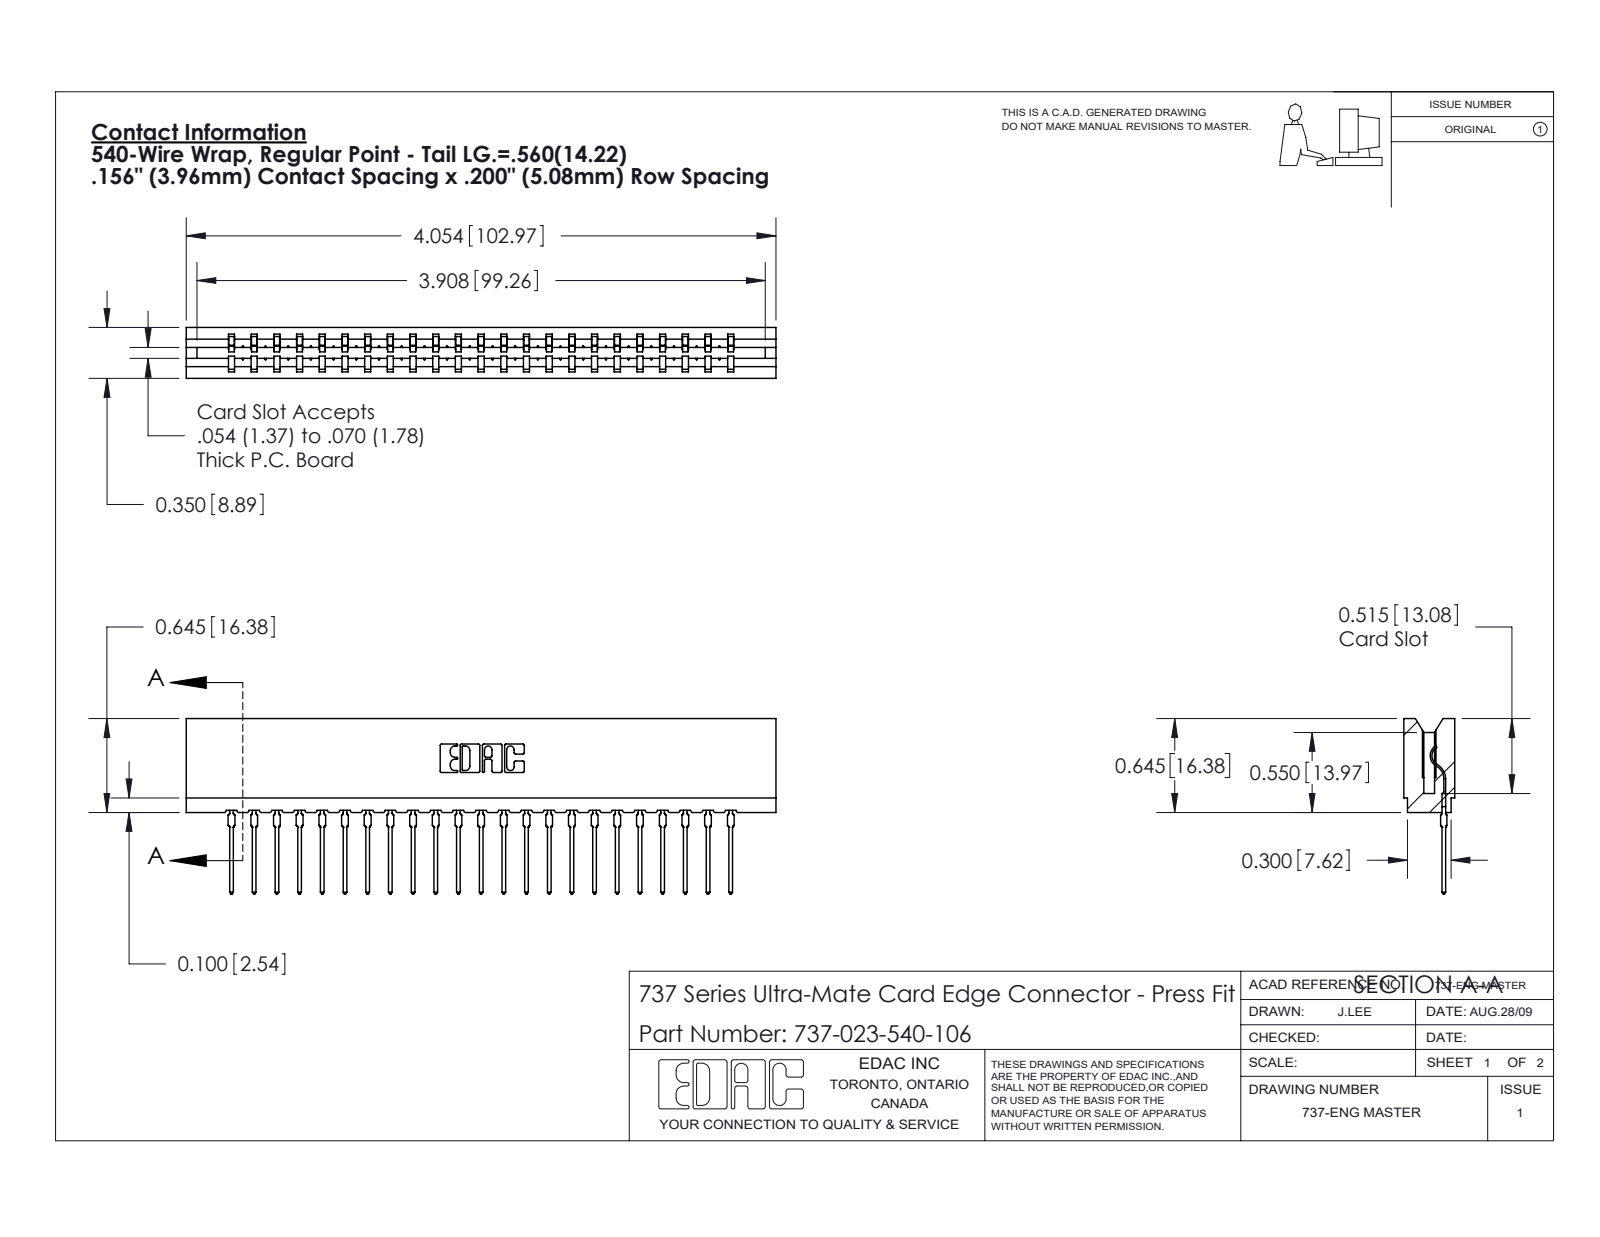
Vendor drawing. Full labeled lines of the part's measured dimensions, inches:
Part name (STEP PRODUCT): 737-023-540-106; 745-292-001_540; 737 Part_Insulator Option - 06
STEP written by: SolidWorks 2020 (CONFIG_CONTROL_DESIGN)
Units: inches
Bodies: 24 solids, 2694 faces (1619 planar, 477 cylindrical, 598 other)
Overall size (bounding box): 4.054 × 1.206 × 0.35
Volume: 0.618 in³ · Surface area: 20.97 in²
Partial cylindrical surfaces — rounded edges, fillets, slot ends (radius × count): R0.015 ×46, R0.021 ×46, R0.01 ×22, R0.007 ×6, R0.031 ×6, R0.005 ×4, R0.011 ×4, R0.026 ×3
Main face-to-face distances: 0.138, 0.212, 0.35, 0.624, 0.156, 0.78, 0.074, 0.468, 0.045, 0.305
